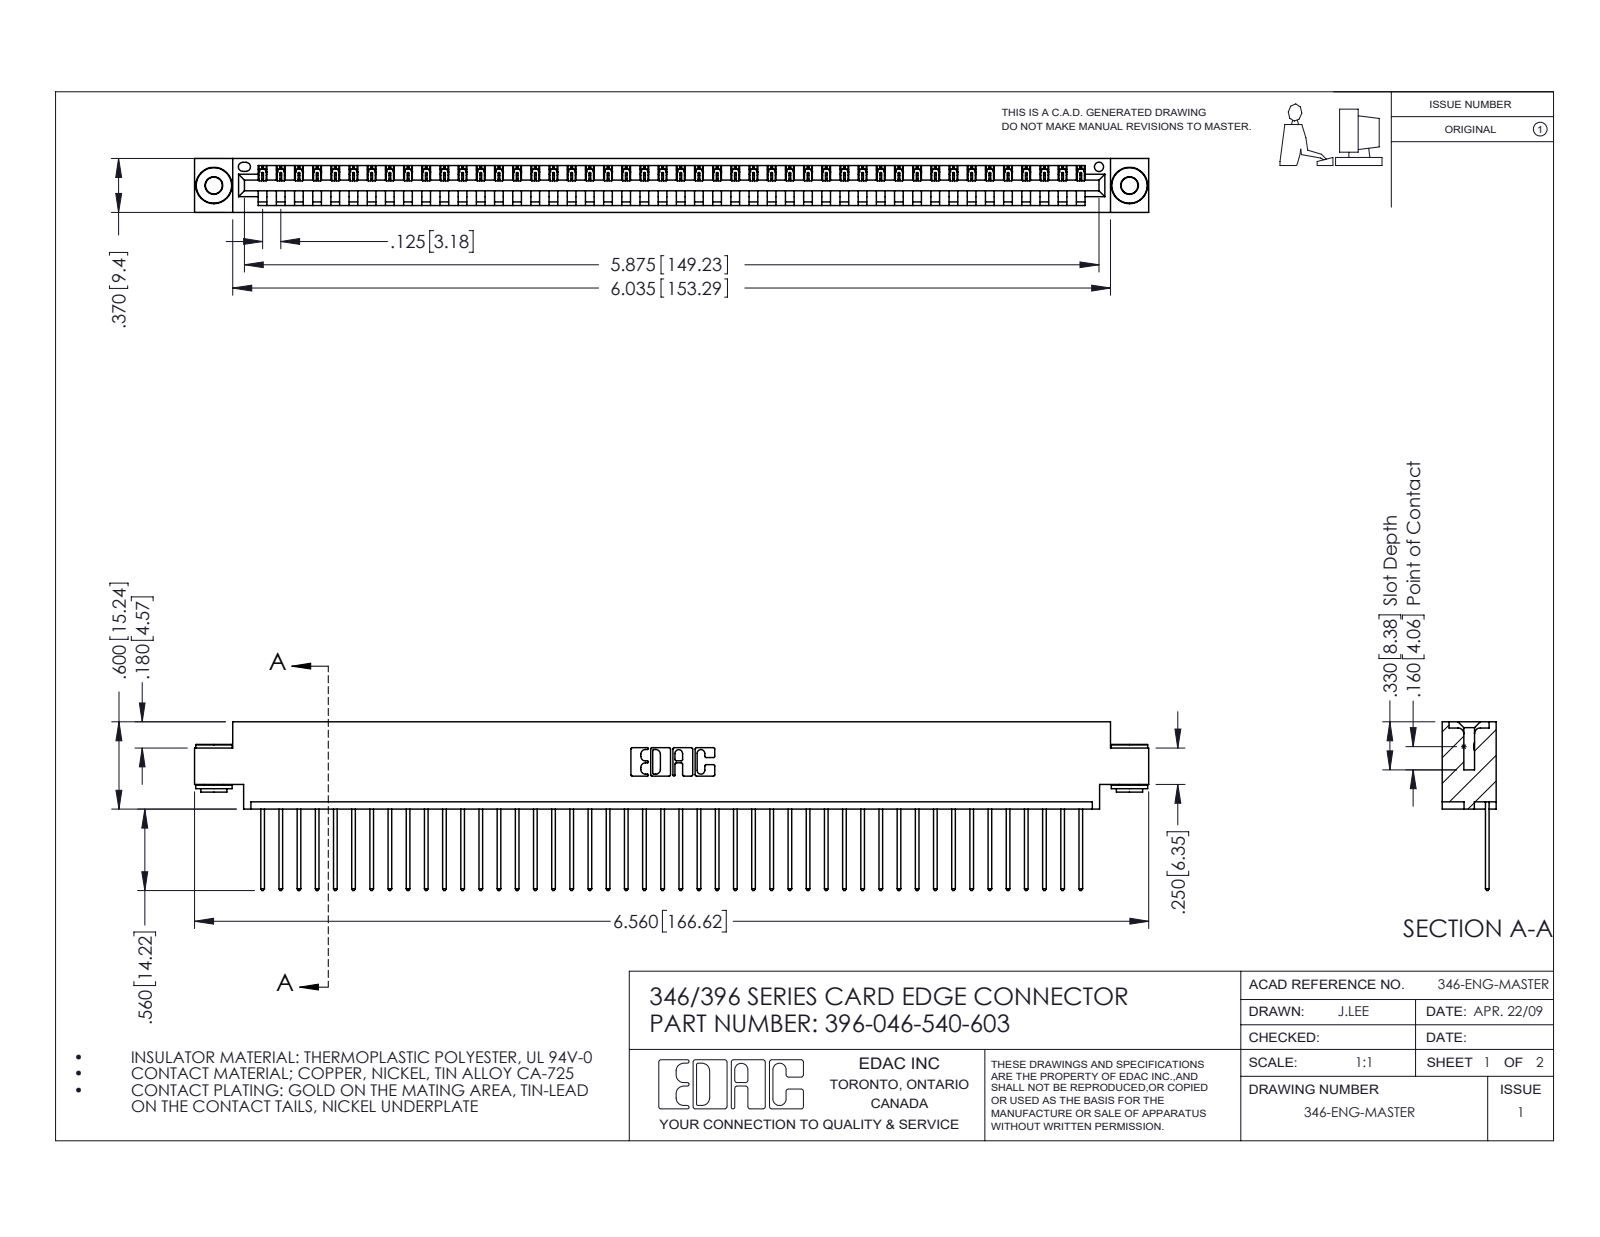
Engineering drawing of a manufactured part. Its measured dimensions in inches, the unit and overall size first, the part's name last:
Units: inches
Overall size (bounding box): 6.56 × 1.16 × 0.37
Round holes (diameter × count): ⌀0.116 ×2, ⌀0.156 ×2, ⌀0.064 ×1
Round bosses / shafts (diameter × count): ⌀0.25 ×2, ⌀0.18 ×2, ⌀0.136 ×2
Partial cylindrical surfaces — rounded edges, fillets, slot ends (radius × count): R0.006 ×92, R0.01 ×92, R0.01 ×22, R0.007 ×6, R0.031 ×6, R0.026 ×3, R0.031 ×2, R0.04 ×2
Main face-to-face distances: 0.048, 0.322, 0.37, 0.25, 0.025, 0.072, 0.298, 0.148, 0.222, 0.1
Hole centre spacings: 0.246, 6.086, 6.295
Volume: 0.971 in³ · Surface area: 32.17 in²
Bodies: 49 solids, 2832 faces (1930 planar, 894 cylindrical, 8 other)
Part name (STEP PRODUCT): 345-250-002_345-250-002-102; 345-292-001_345-293-140; 346 Part_0.170 Offset - 0.156 Dia-TH; 396-046-540-603
STEP written by: SolidWorks 2016 (CONFIG_CONTROL_DESIGN)
